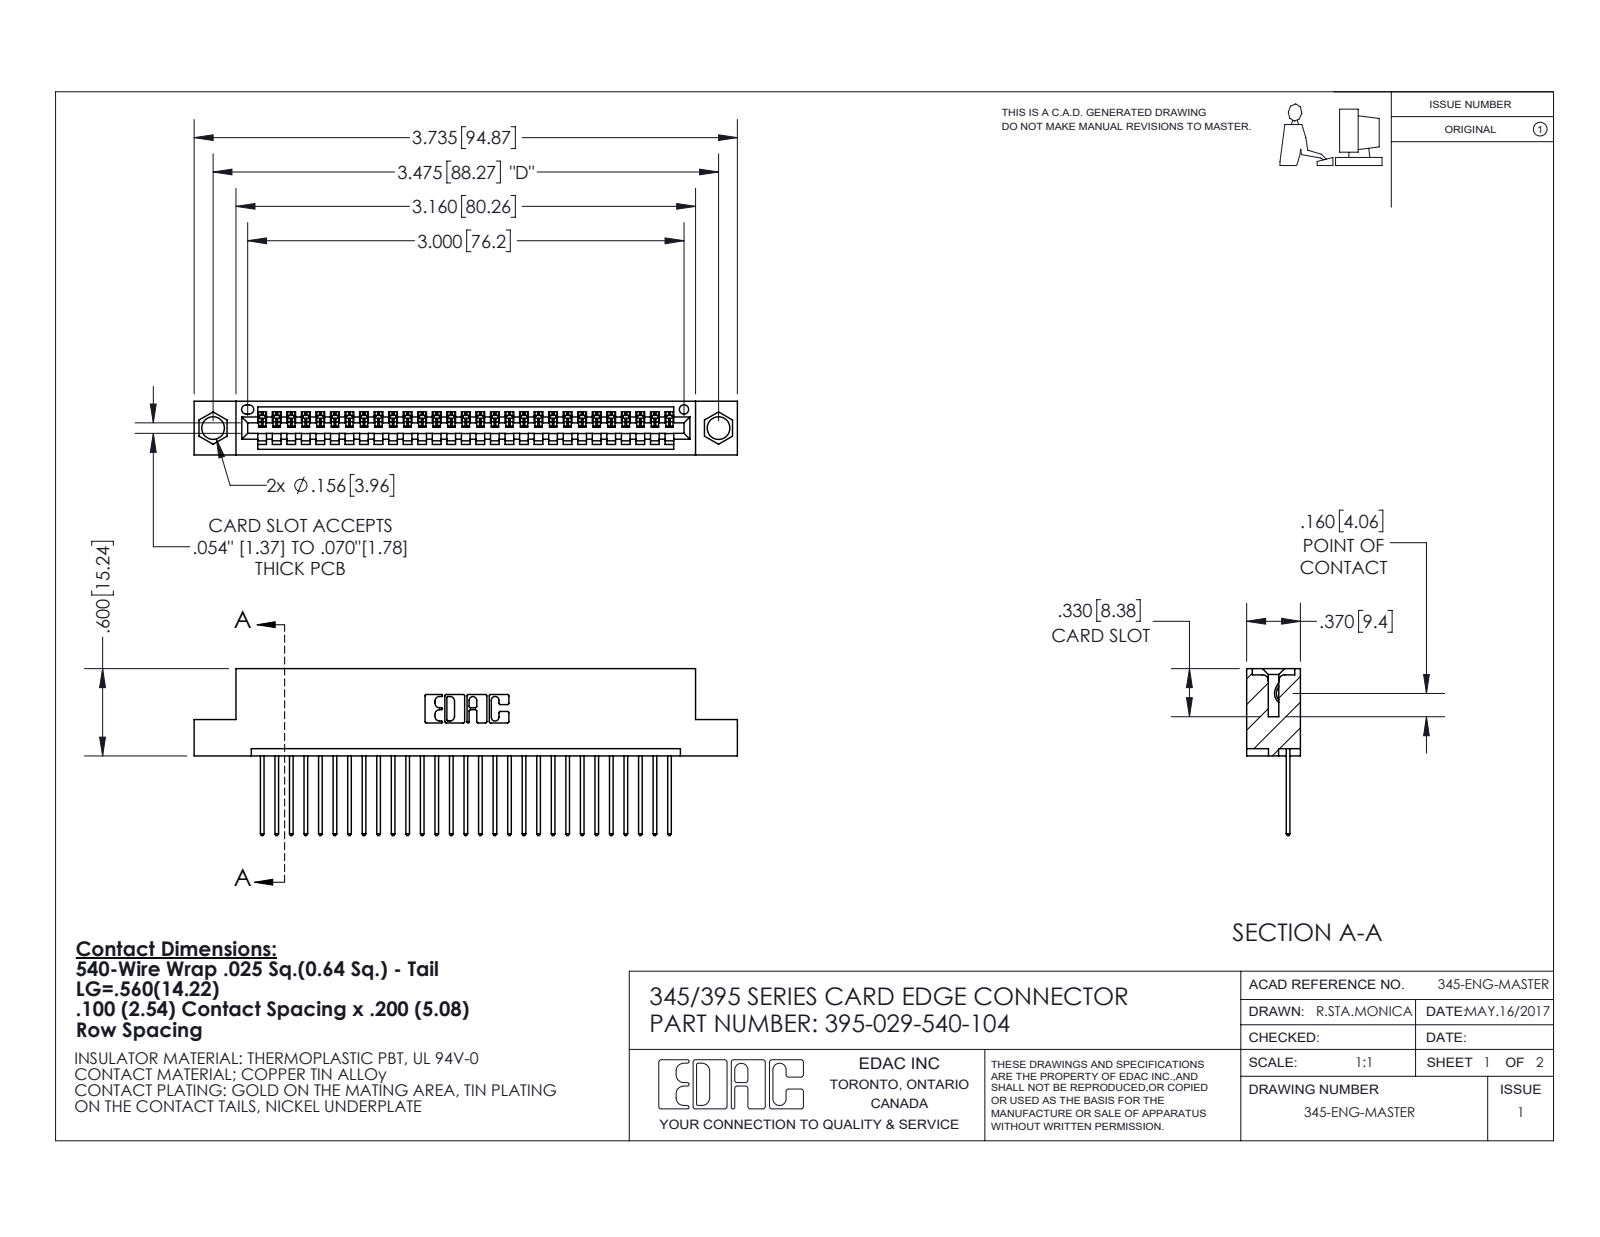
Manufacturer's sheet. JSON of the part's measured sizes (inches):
{"part_name": "395-029-540-104; 345 Part_Flush Mounting Lugs - 0.156 Dia-TI; 345-292-001_345-293-140", "step_written_by": "SolidWorks 2020 (CONFIG_CONTROL_DESIGN)", "units": "inches", "bodies": {"solids": 30, "faces": 1822, "planar": 1254, "cylindrical": 568, "other": 0}, "overall_size": [3.735, 1.147, 0.37], "volume_in3": 0.539, "surface_area_in2": 18.12, "round_holes": [[0.156, 2], [0.064, 1]], "partial_cylinders_radius": [[0.006, 58], [0.01, 58], [0.01, 22], [0.007, 6], [0.031, 6], [0.026, 3], [0.031, 2], [0.04, 2]], "face_to_face_distances": [0.298, 0.072, 0.2, 0.37, 0.098, 0.272, 0.025, 0.225, 0.149, 0.072], "hole_center_spacings": [0.27, 3.24, 3.475]}
